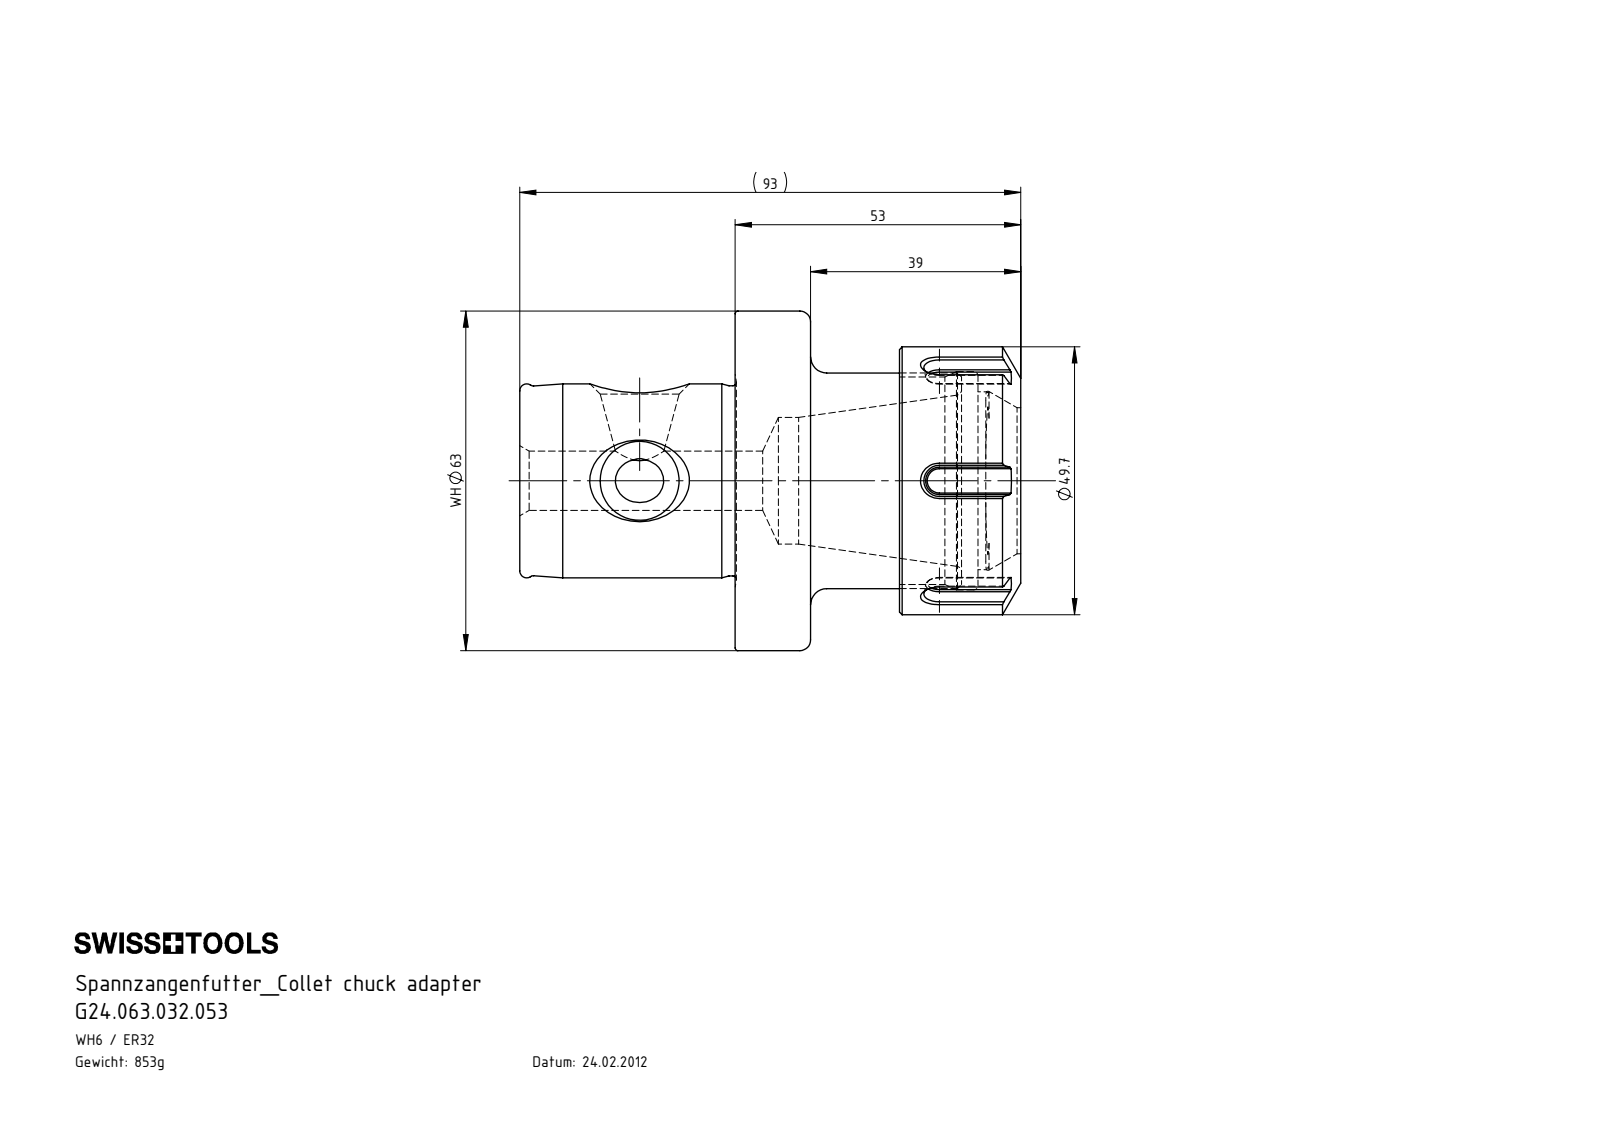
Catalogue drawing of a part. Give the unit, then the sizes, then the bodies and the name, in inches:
Units: inches
Overall size (bounding box): 3.661 × 2.48 × 2.48
Round holes (diameter × count): ⌀0.433 ×1, ⌀0.925 ×1, ⌀1.067 ×1, ⌀1.516 ×1, ⌀1.594 ×1
Round bosses / shafts (diameter × count): ⌀2.48 ×1, ⌀1.957 ×1, ⌀1.575 ×1, ⌀1.417 ×1, ⌀1.39 ×1
Partial cylindrical surfaces — rounded edges, fillets, slot ends (radius × count): R0.61 ×2
Main face-to-face distances: 0.551, 1.575, 2.126, 2.776, 1.201, 0.65, 3.661, 2.087, 1.535, 0.886
Volume: 6.631 in³ · Surface area: 45.89 in²
Bodies: 2 solids, 152 faces (55 planar, 23 cylindrical, 74 other)
Part name (STEP PRODUCT): WH6.E32.K01.053; E32-ER1.001.022; WH6-E32.K01.053
STEP written by: SolidWorks 2022 (AUTOMOTIVE_DESIGN)
